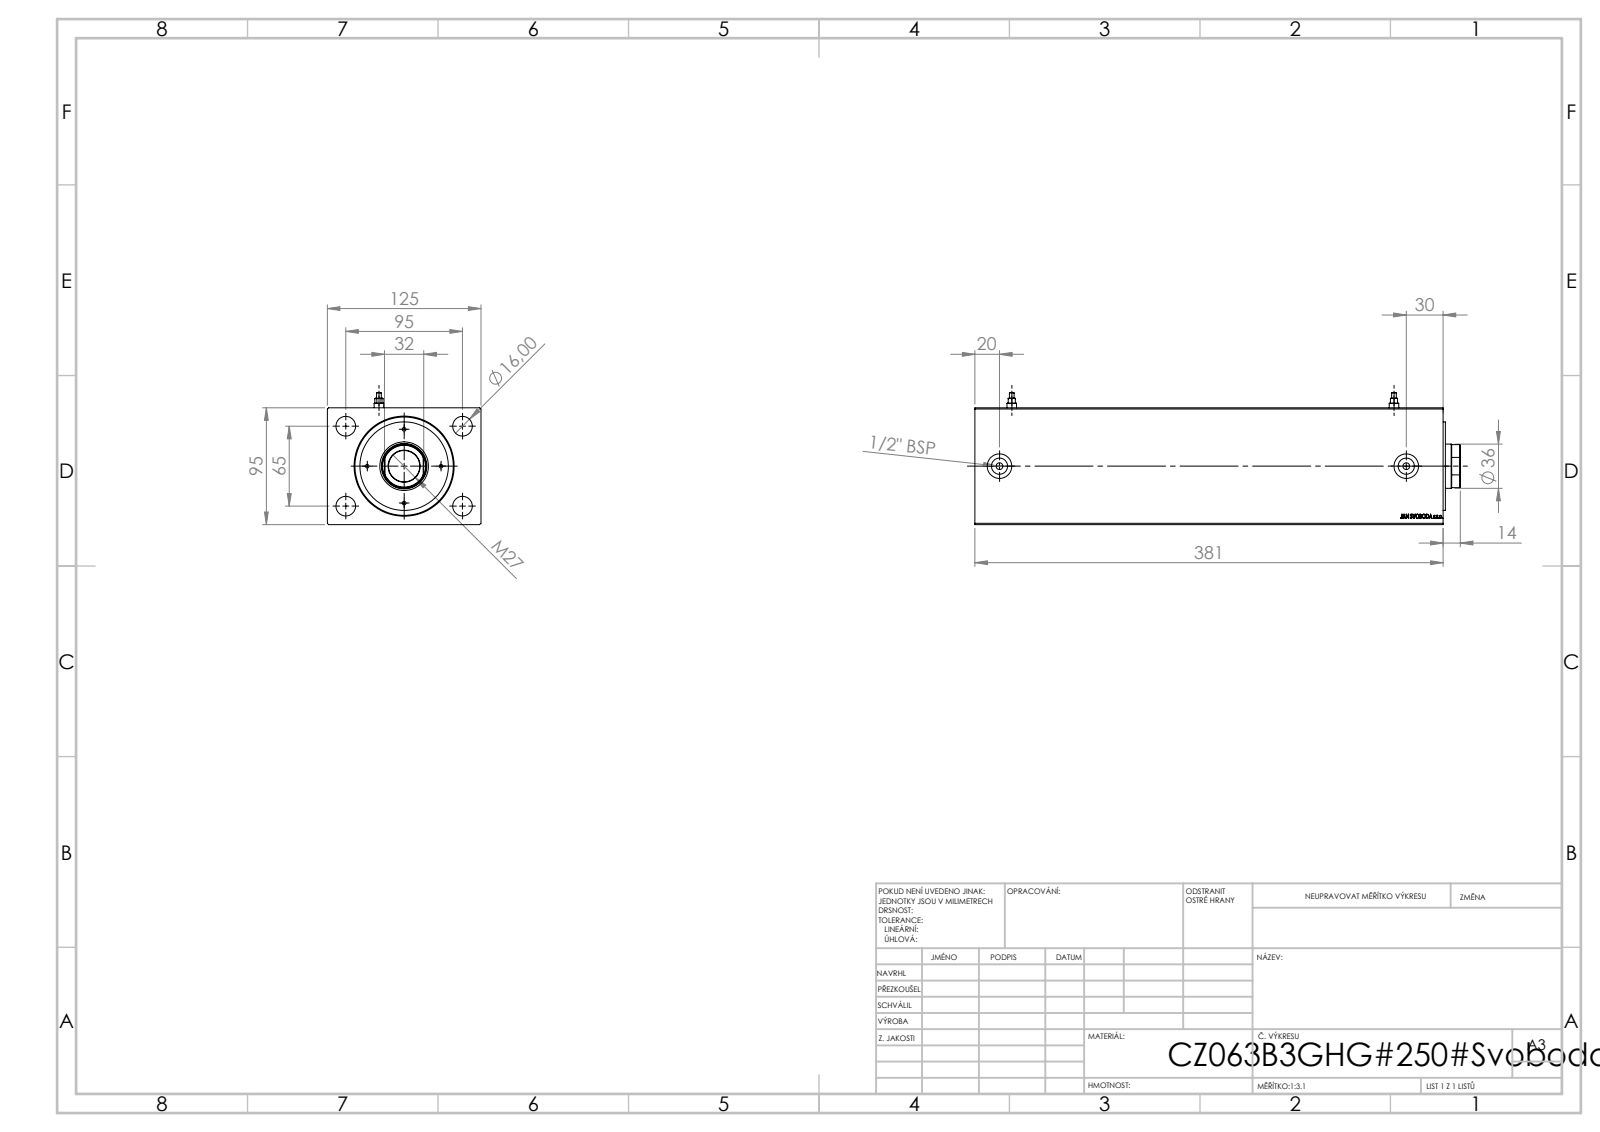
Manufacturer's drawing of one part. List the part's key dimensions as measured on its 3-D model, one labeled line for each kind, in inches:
Part name (STEP PRODUCT): V500CZ_B_VC; V500CZ; Zatka_Cushioning3
STEP written by: SolidWorks 2019 (CONFIG_CONTROL_DESIGN)
Units: inches
Bodies: 5 solids, 934 faces (424 planar, 74 cylindrical, 436 other)
Overall size (bounding box): 15.551 × 4.921 × 4.232
Volume: 240.5 in³ · Surface area: 539.3 in²
Round holes (diameter × count): ⌀0.118 ×4, ⌀0.63 ×4, ⌀0.071 ×2, ⌀0.217 ×2, ⌀0.315 ×2, ⌀0.518 ×2, ⌀0.787 ×2, ⌀1.004 ×1, ⌀1.417 ×1, ⌀1.457 ×1, ⌀2.48 ×1, ⌀3.15 ×1
Round bosses / shafts (diameter × count): ⌀0.307 ×2, ⌀0.15 ×2, ⌀2.835 ×1
Partial cylindrical surfaces — rounded edges, fillets, slot ends (radius × count): R0.689 ×1
Main face-to-face distances: 3.74, 4.921, 15, 14.181, 0.819, 0.551, 0.071, 0.48, 13.701, 14.52
Hole centre spacings: 1.181, 1.453, 1.67, 1.873, 2.266, 3.091, 3.309, 2.362
